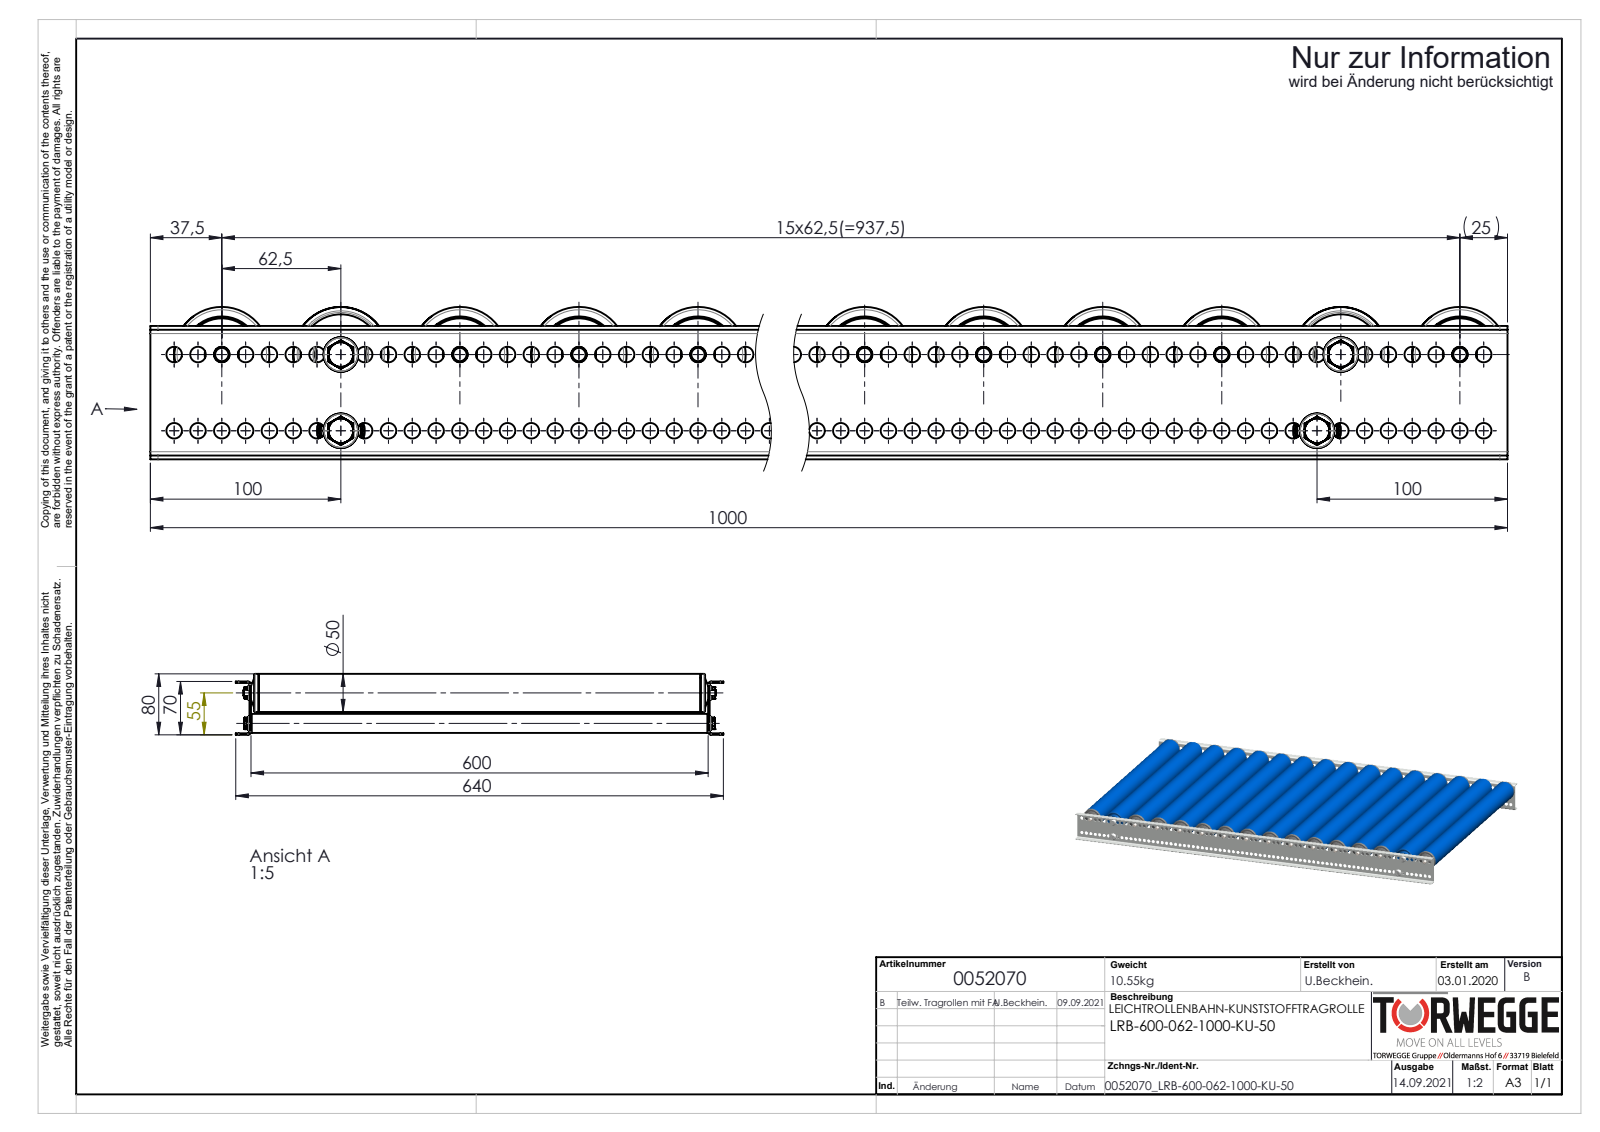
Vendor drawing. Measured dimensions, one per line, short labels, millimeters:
name: Druckfeder_1,2x10x30; KUT100-50x2,8-KB-A8-FA_KFG_0034516_KUT100-50x2,8-KB-A8-FA-EL=600; S100994_Sperrzahnschraube_M08x16-8.8-A2K; 0017015_Tragrollenrohr-Ø50x2,8KU_KFG_0017015_L=585 (+8 more)
written by: SolidWorks 2020 (AUTOMOTIVE_DESIGN)
unit: mm
bodies: 274 solids, 5068 faces (1336 planar, 2192 cylindrical, 1540 other)
size: 1000 × 640 × 80
volume: 5 871 000 mm³; area: 4 286 000 mm²
holes: 158× ⌀8.2, 14× ⌀7.6, 14× ⌀8, 14× ⌀25, 14× ⌀30, 14× ⌀35, 14× ⌀39.4, 14× ⌀40, 4× ⌀6.8, 2× ⌀12, 2× ⌀12.1, 2× ⌀16
bosses: 16× ⌀50, 14× ⌀44.4, 14× ⌀38, 14× ⌀36, 14× ⌀33, 14× ⌀22, 14× ⌀21, 4× ⌀25
rounds: 28× R0.6, 28× R0.75, 28× R2.45, 14× R4.87, 14× R7, 8× R4, 4× R2, 4× R2.5
face distances: 2, 602, 68, 600, 604, 592, 66, 70, 12, 6
hole spacings: 12.5, 25, 37.5, 50, 62.5, 75, 87.5, 100
